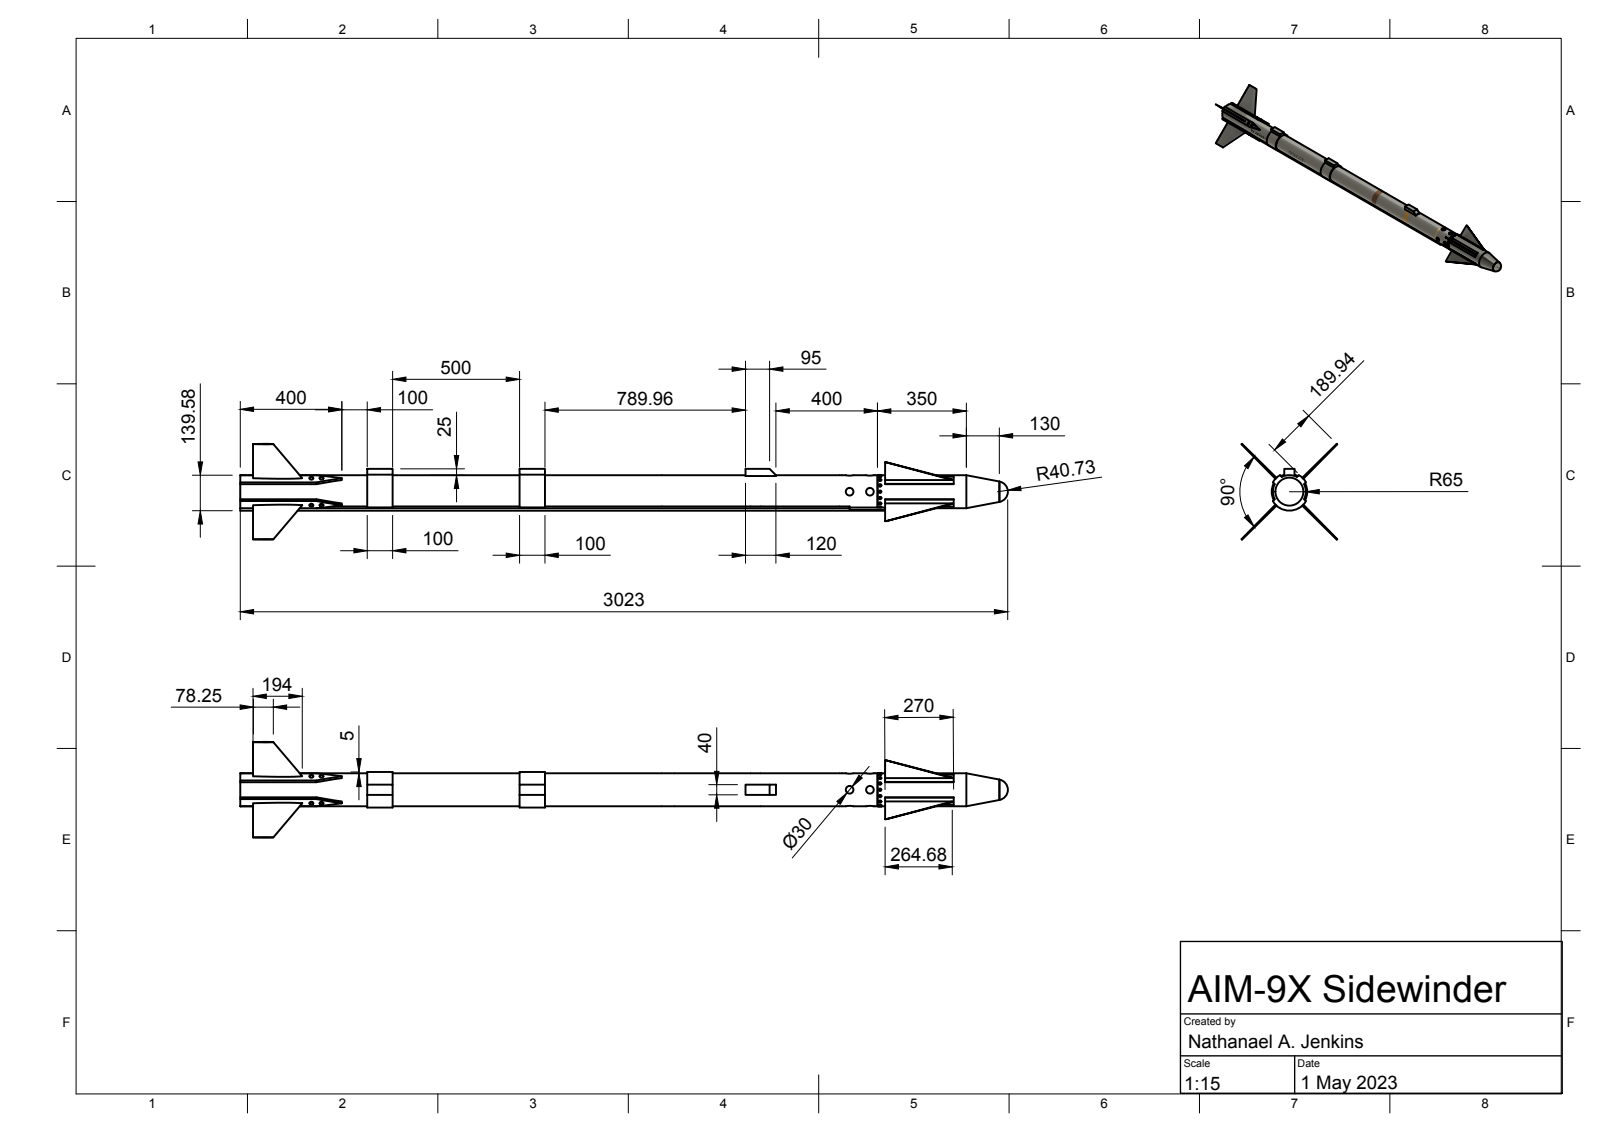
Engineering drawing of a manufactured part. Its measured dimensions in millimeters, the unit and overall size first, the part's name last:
Units: millimetres
Overall size (bounding box): 3023 × 658.22 × 376.44
Round holes (diameter × count): ⌀30 ×4, ⌀20 ×1, ⌀110 ×1
Round bosses / shafts (diameter × count): ⌀10 ×44, ⌀130 ×1
Partial cylindrical surfaces — rounded edges, fillets, slot ends (radius × count): R65 ×12, R15 ×5, R70 ×1, R74.58 ×1
Main face-to-face distances: 30, 15, 5, 120, 135, 40, 250, 385, 370, 35
Hole centre spacings: 80
Volume: 58 560 000 mm³ · Surface area: 3 177 000 mm²
Bodies: 6 solids, 354 faces (175 planar, 126 cylindrical, 53 other)
Part name (STEP PRODUCT): AIM-9X Sidewinder v21
STEP written by: Autodesk Translation Framework v12.4.0.73 (AUTOMOTIVE_DESIGN)
